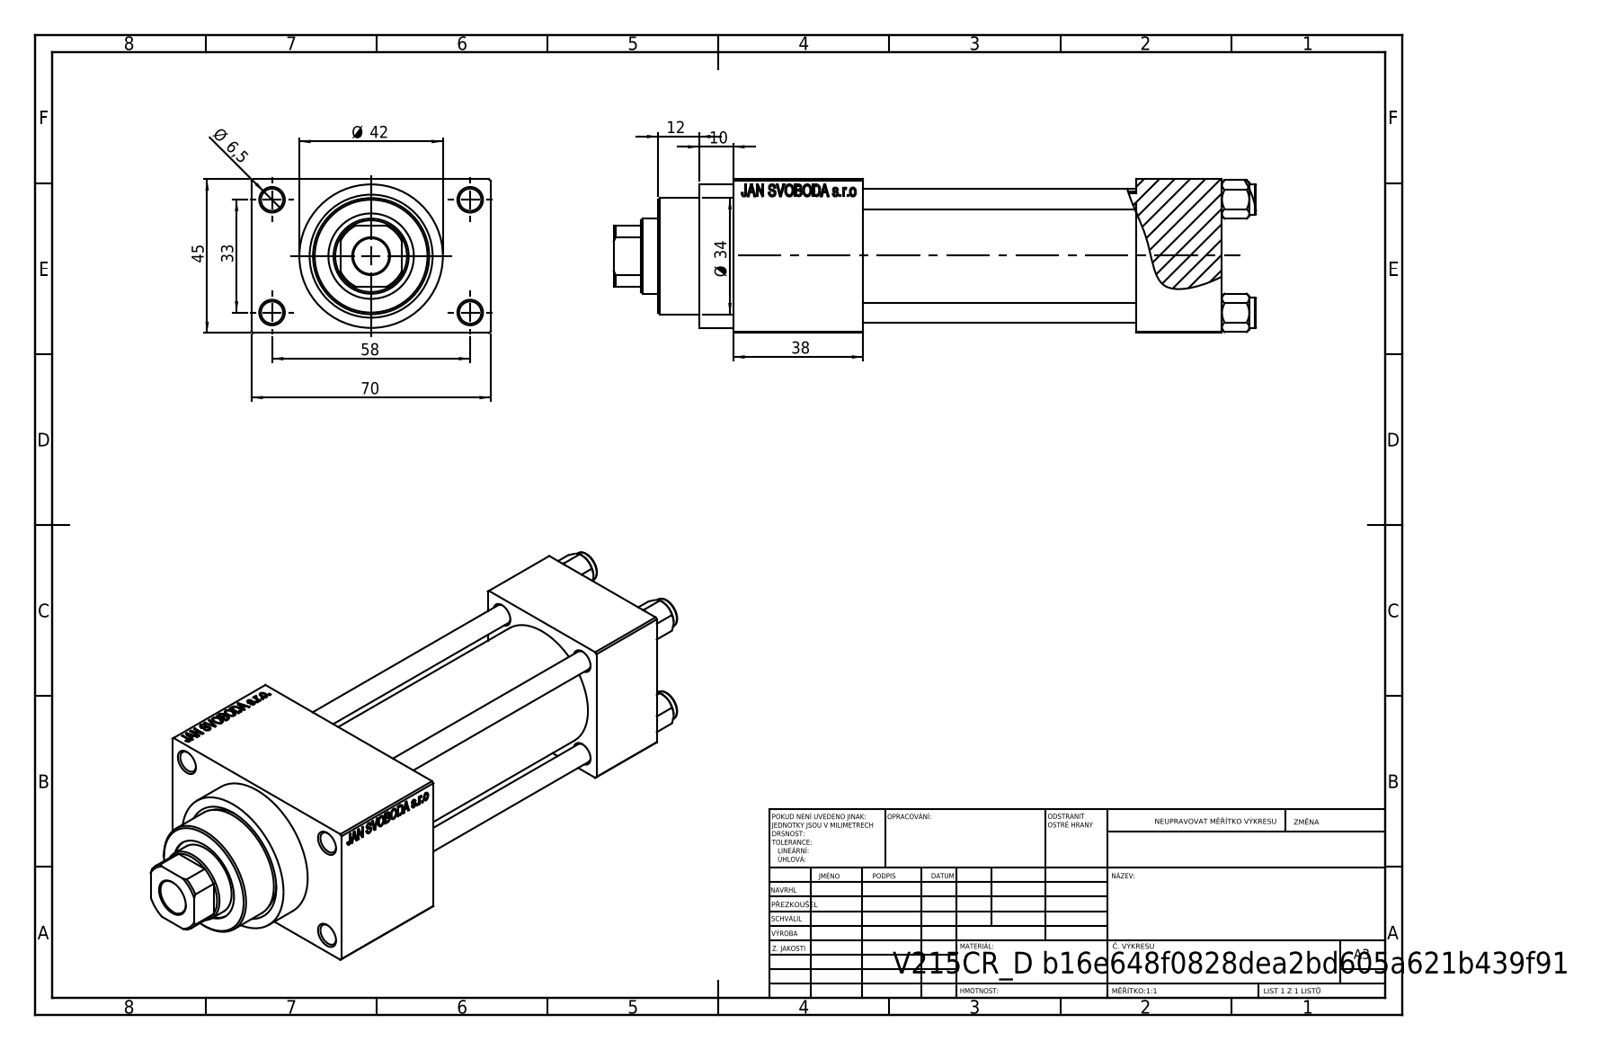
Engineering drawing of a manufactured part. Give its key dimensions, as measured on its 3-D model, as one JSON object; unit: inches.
{"part_name": "V215CR_D_Body; V215CR_VCP_D; V215_VC_A; NUT_M5_D (+1 more)", "step_written_by": "SolidWorks 2019 (CONFIG_CONTROL_DESIGN)", "units": "inches", "bodies": {"solids": 11, "faces": 1104, "planar": 496, "cylindrical": 88, "other": 520}, "overall_size": [7.402, 2.756, 1.772], "volume_in3": 16.33, "surface_area_in2": 140.8, "round_holes": [[0.236, 4], [0.256, 4], [0.276, 2], [0.518, 2], [0.787, 2], [0.413, 1], [0.866, 1], [0.945, 1], [0.984, 1], [1.26, 1], [1.299, 1]], "round_bosses_or_shafts": [[0.354, 4], [1.654, 1], [1.496, 1], [1.339, 1]], "partial_cylinders_radius": [[0.413, 1]], "face_to_face_distances": [1.772, 0.984, 0.492, 3.15, 4.134, 2.264, 4.646, 1.496, 5.63, 2.756], "hole_center_spacings": [0.488, 0.924, 1.307, 1.314, 1.392, 1.795, 2.219, 1.299]}
